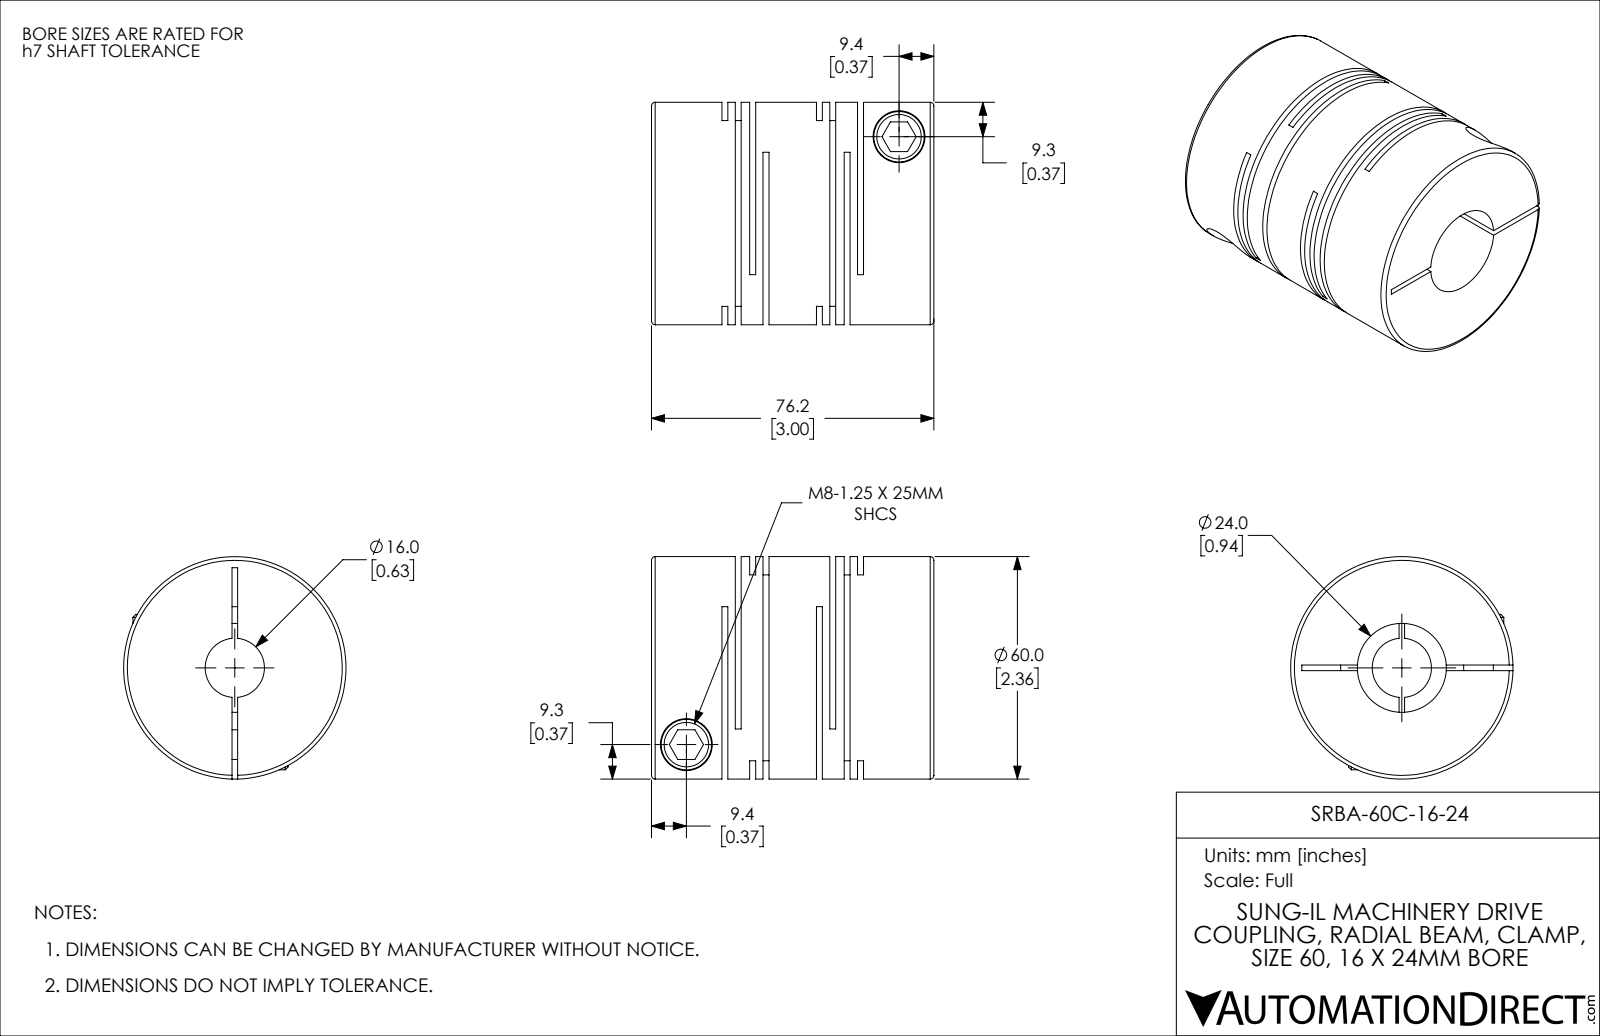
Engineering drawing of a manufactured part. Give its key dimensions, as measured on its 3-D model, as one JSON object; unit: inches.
{"part_name": "SRBA-60C-16-24", "step_written_by": "SolidWorks 2021 (CONFIG_CONTROL_DESIGN)", "units": "inches", "bodies": {"solids": 1, "faces": 115, "planar": 60, "cylindrical": 42, "other": 13}, "overall_size": [3, 2.362, 2.362], "volume_in3": 9.538, "surface_area_in2": 89.06, "round_holes": [[0.315, 2], [0.551, 2], [0.63, 1], [0.945, 1]], "round_bosses_or_shafts": [[0.535, 2], [2.362, 1]], "face_to_face_distances": [0.063, 0.142, 0.295, 1.004, 1.299, 1.067, 0.232, 0.941, 0.709, 0.079]}
